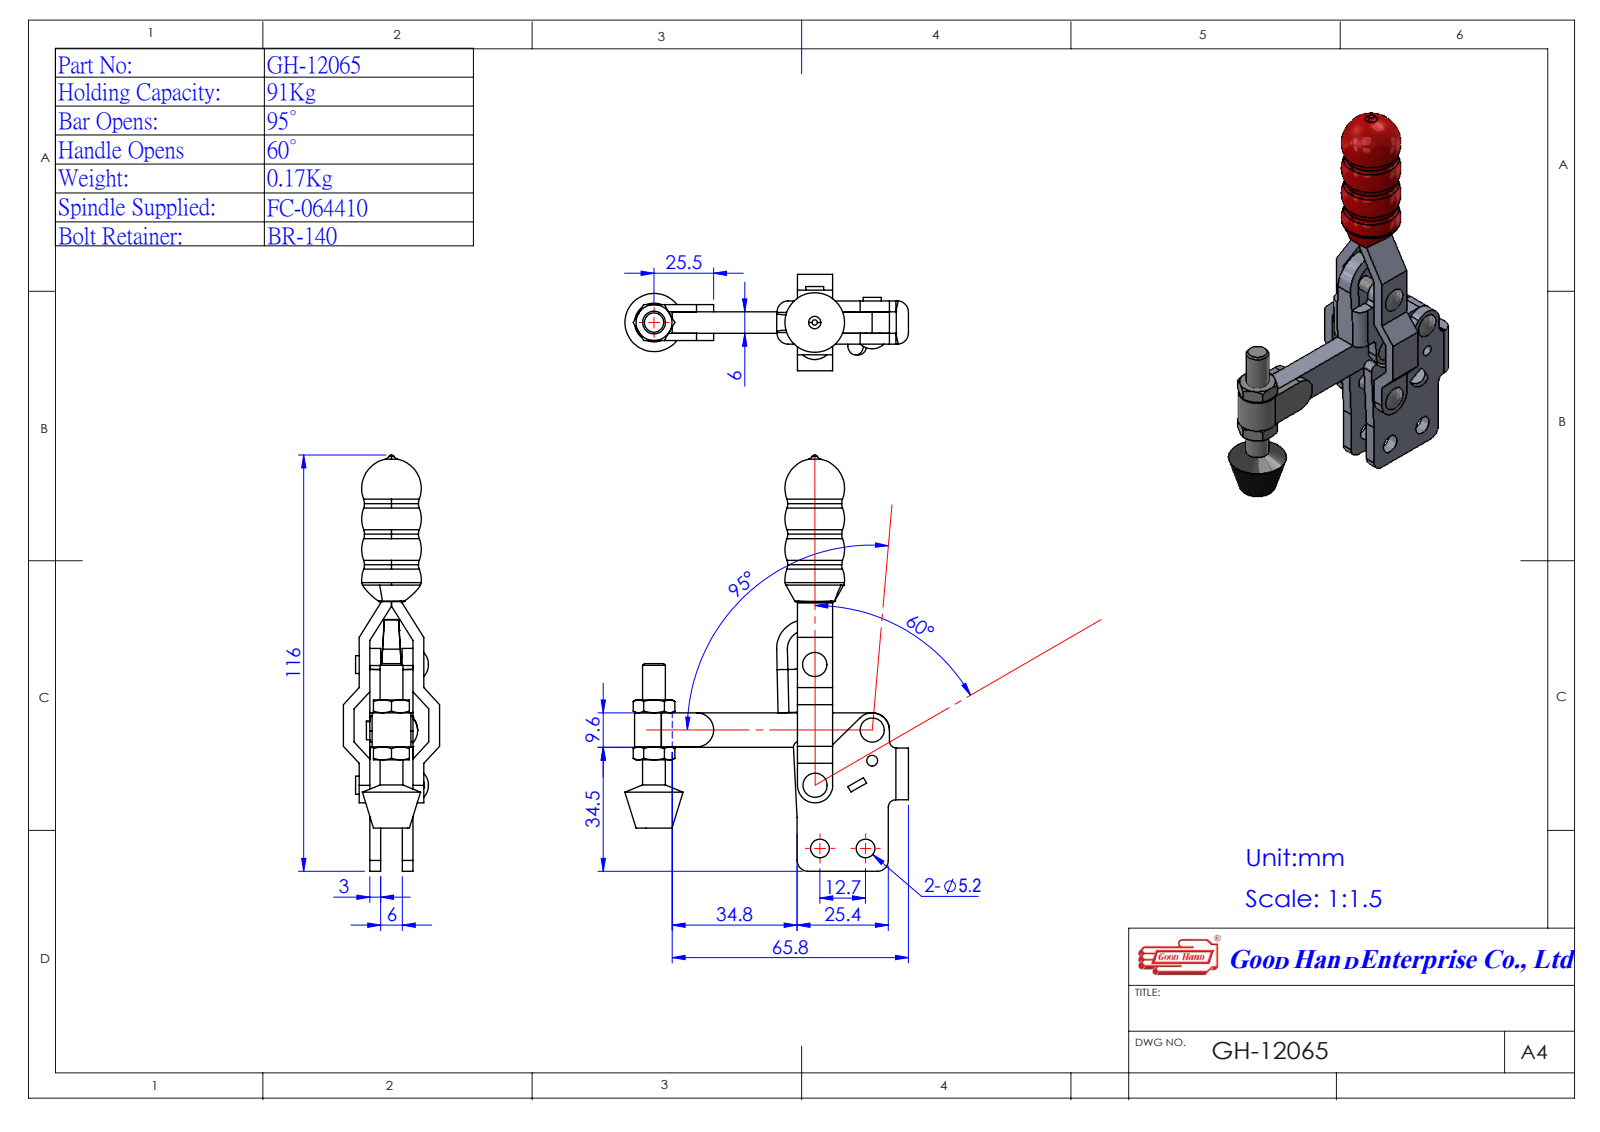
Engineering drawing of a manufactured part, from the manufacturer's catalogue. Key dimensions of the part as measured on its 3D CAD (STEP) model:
Part name (STEP PRODUCT): Group4_112055U13-1^GH-12065(簡化); GH-12065(簡化); 11206008_00-1^GH-12065(簡化); Group1_112055U01 (+2 more)
STEP written by: SolidWorks 2016 (AUTOMOTIVE_DESIGN)
Units: millimetres
Bodies: 5 solids, 302 faces (112 planar, 122 cylindrical, 68 other)
Overall size (bounding box): 115.85 × 80.65 × 26.8
Volume: 27 286 mm³ · Surface area: 17 802 mm²
Round holes (diameter × count): ⌀3 ×6, ⌀5.2 ×2
Round bosses / shafts (diameter × count): ⌀5 ×4, ⌀6.35 ×1
Partial cylindrical surfaces — rounded edges, fillets, slot ends (radius × count): R0.5 ×5, R3 ×4, R3.1 ×4, R0.1 ×2, R1 ×2, R2 ×2, R2.02 ×2, R4.5 ×2
Main face-to-face distances: 3, 9.01, 9, 6, 12.01, 12, 3.01, 6.01, 2.99, 4.4
Hole centre spacings: 17.75, 8.4, 8.5, 12.7, 15.22, 15.38, 15.58, 17.41
